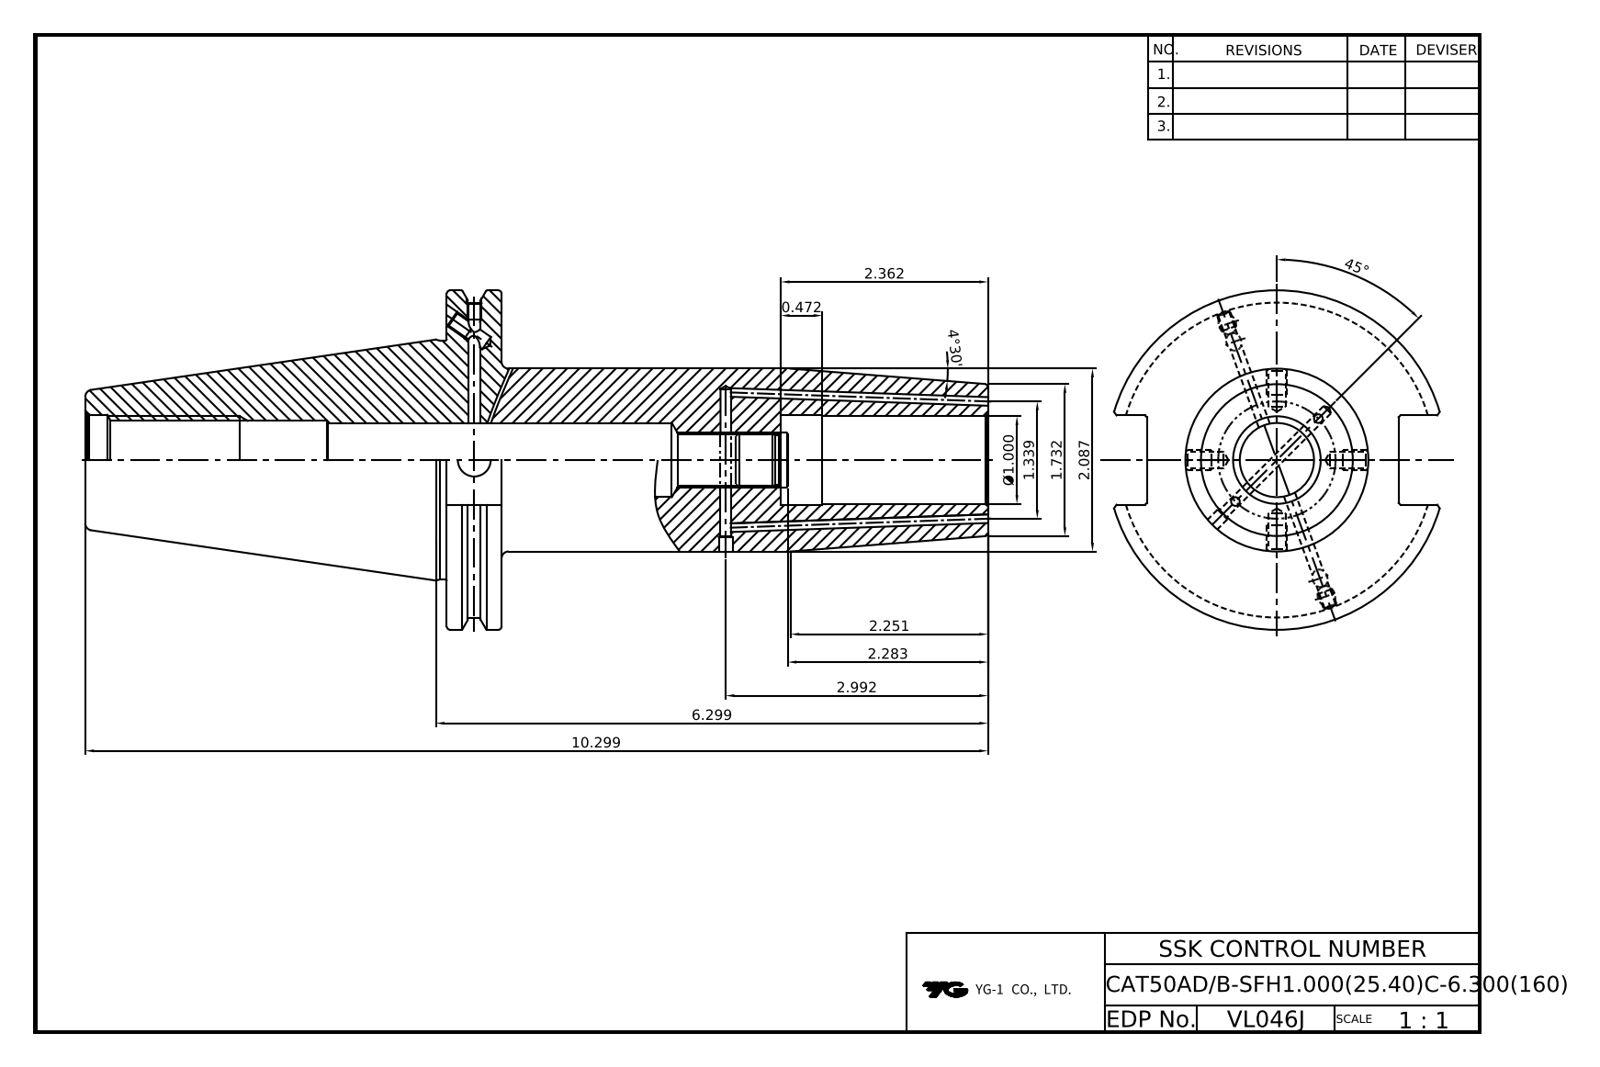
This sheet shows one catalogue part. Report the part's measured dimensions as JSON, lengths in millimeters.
{"part_name": "LO-CAT50ADB-SFH25.4C-160", "step_written_by": "Autodesk Inventor 2025 (AUTOMOTIVE_DESIGN)", "units": "millimeters", "bodies": {"solids": 1, "faces": 88, "planar": 37, "cylindrical": 28, "other": 23}, "overall_size": [261.6, 98.42, 94.69], "volume_mm3": 554774, "surface_area_mm2": 77290, "round_holes": [[2.5, 2], [3.24, 2], [4.13, 2], [4.2, 2], [5, 2], [9.53, 1], [14.92, 1], [21.97, 1], [25.4, 1], [26.2, 1], [26.6, 1]], "round_bosses_or_shafts": [[98.42, 1], [91.29, 1], [69.25, 1], [53, 1]], "face_to_face_distances": [15.88, 156.83, 140.95, 104.77, 120.65, 261.6, 201.6, 96.83, 80.95, 60]}
